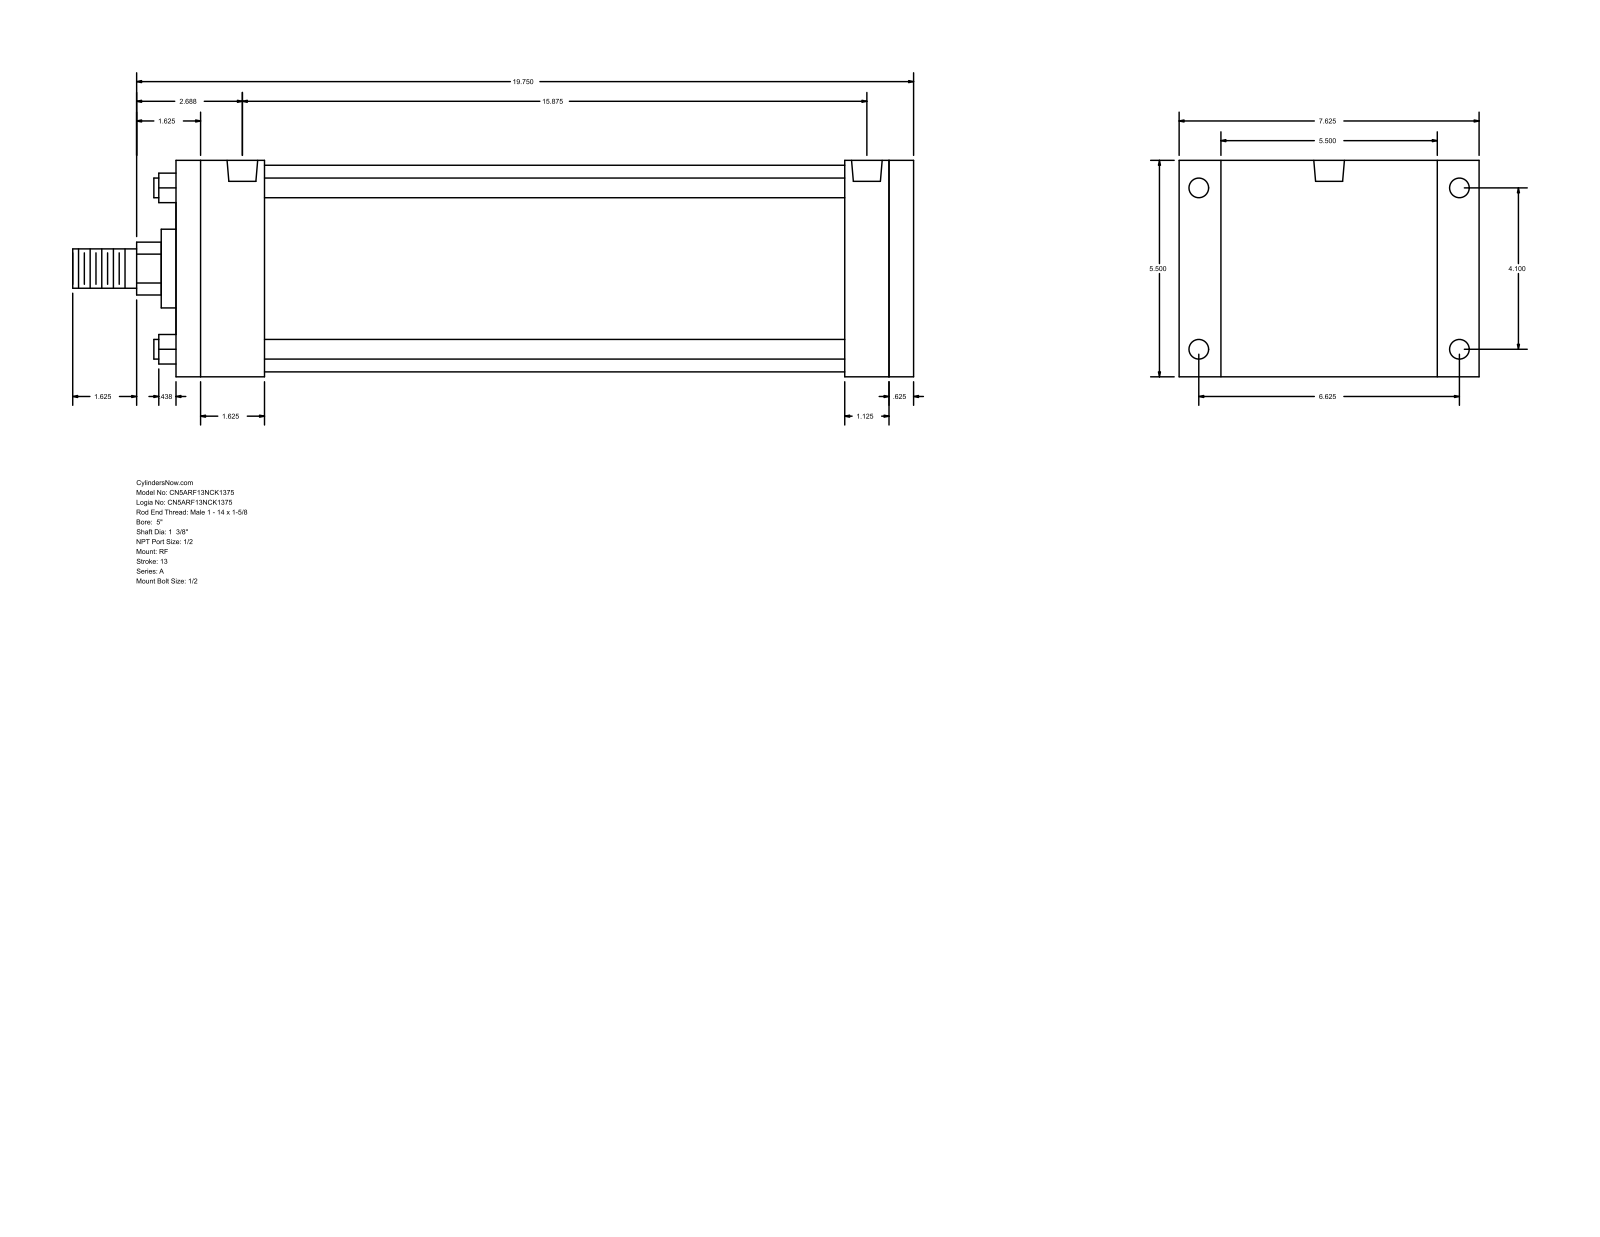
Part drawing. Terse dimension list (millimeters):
name: A_RF__0500_1.375
written by: GSSL Pune (CONFIG_CONTROL_DESIGN)
unit: mm
bodies: 0 solids, 92 faces (64 planar, 28 cylindrical, 0 other)
size: 542.92 × 193.68 × 139.7
holes: 4× ⌀8.73, 4× ⌀12.7, 2× ⌀19.77
bosses: 4× ⌀12.7, 1× ⌀133.35, 1× ⌀50.8, 1× ⌀34.92, 1× ⌀25.4
rounds: 1× R17.06
face distances: 139.7, 476.25, 15.88, 460.37, 57.15, 403.22, 419.1, 431.8, 374.65, 28.57
hole spacings: 2.39, 104.14, 168.28, 197.9, 398.45, 400.84, 403.23
